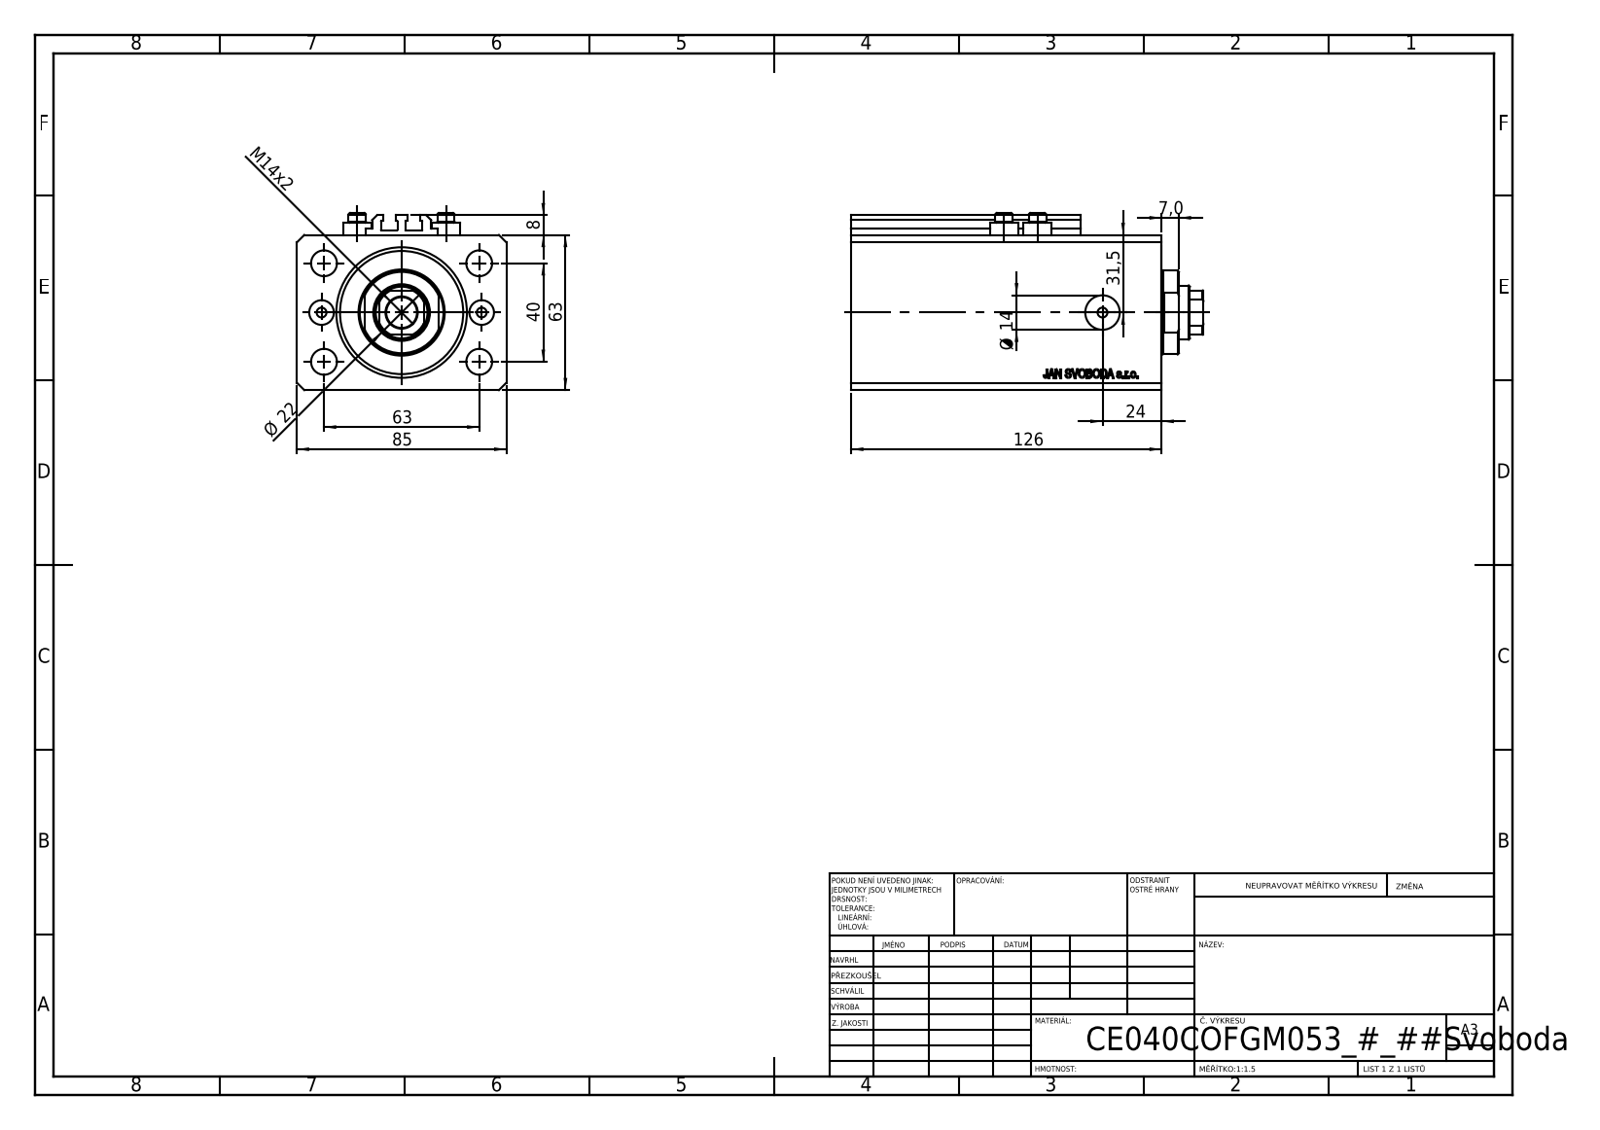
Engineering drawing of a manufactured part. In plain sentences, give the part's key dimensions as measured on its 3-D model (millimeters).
The part is named "V250CE_C_Body; ALLEN BOLT V250CE; V250CE_C_VCP; V250CE_VC_C". Its 3-D file was written by "SolidWorks 2019 (CONFIG_CONTROL_DESIGN)". It is 8 solids with 1034 faces: 504 planar, 86 cylindrical and 444 other. Overall it measures 143 by 85 by 72 millimeters. Its volume is 600 065 cubic millimeters and its surface area 115 837 square millimeters. Round holes: 8 of diameter 4, 4 of diameter 10.5, 2 of diameter 10, 2 of diameter 14, 1 of diameter 12.5, 1 of diameter 22, 1 of diameter 40, 1 of diameter 53. Round bosses or shafts: 4 of diameter 11.6, 4 of diameter 7, 1 of diameter 34. Partial cylindrical surfaces (rounded edges, fillets, slot ends): 10 of radius 0.2, 1 of radius 10.5. The main face-to-face distances are 63, 85, 126, 17, 109, 11.4, 97.6, 114.6, 2.5, 10. The hole center spacings are 20.02, 37.31, 67.05, 13.6, 32.5, 36, 38.48, 40.
